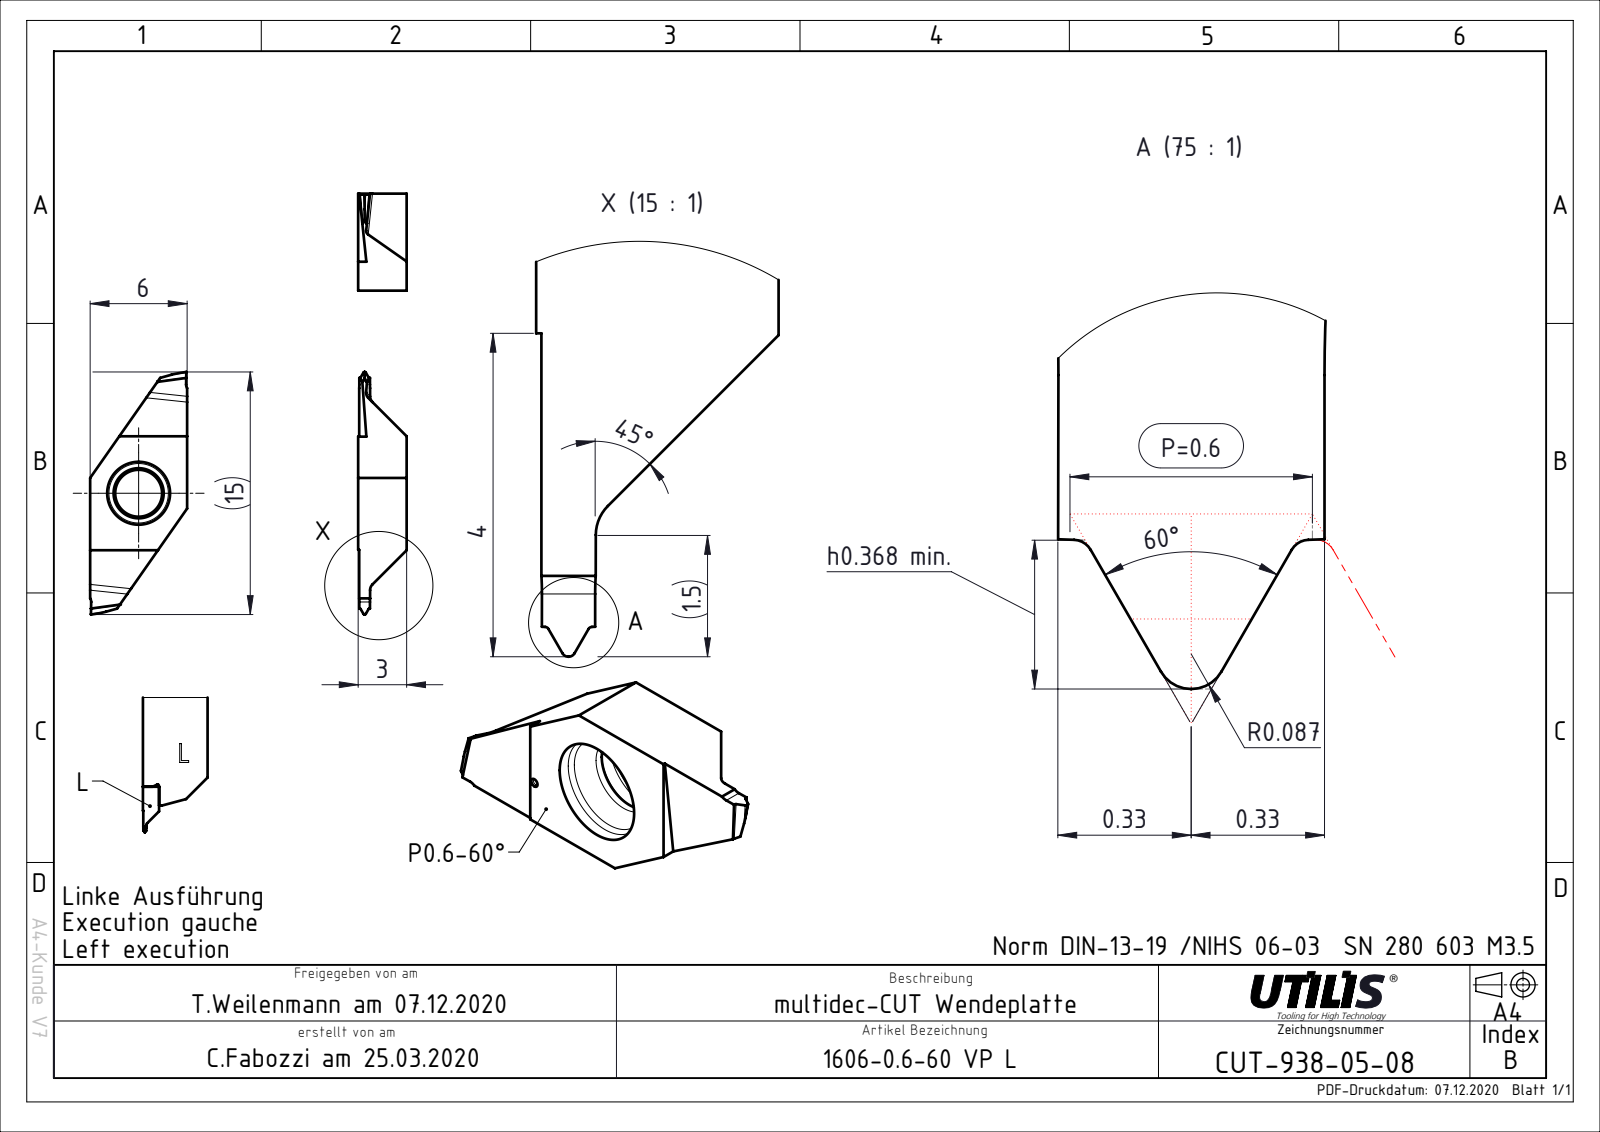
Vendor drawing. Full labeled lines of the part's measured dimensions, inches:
Part name (STEP PRODUCT): CUT-938-05; ASME Y14.5
STEP written by: FormatWorks Professional (AP242_MANAGED_MODEL_BASED_3D_ENGINEERING_MIM_LF)
Units: inches
Bodies: 1 solid, 42 faces (24 planar, 14 cylindrical, 4 other)
Overall size (bounding box): 0.591 × 0.236 × 0.118
Volume: 0.008 in³ · Surface area: 0.326 in²
Round holes (diameter × count): ⌀0.114 ×1
Partial cylindrical surfaces — rounded edges, fillets, slot ends (radius × count): R0.02 ×2
Main face-to-face distances: 0.236, 0.118, 0.02, 0.354, 0.441, 0.441, 0.472, 0.276, 0.504
